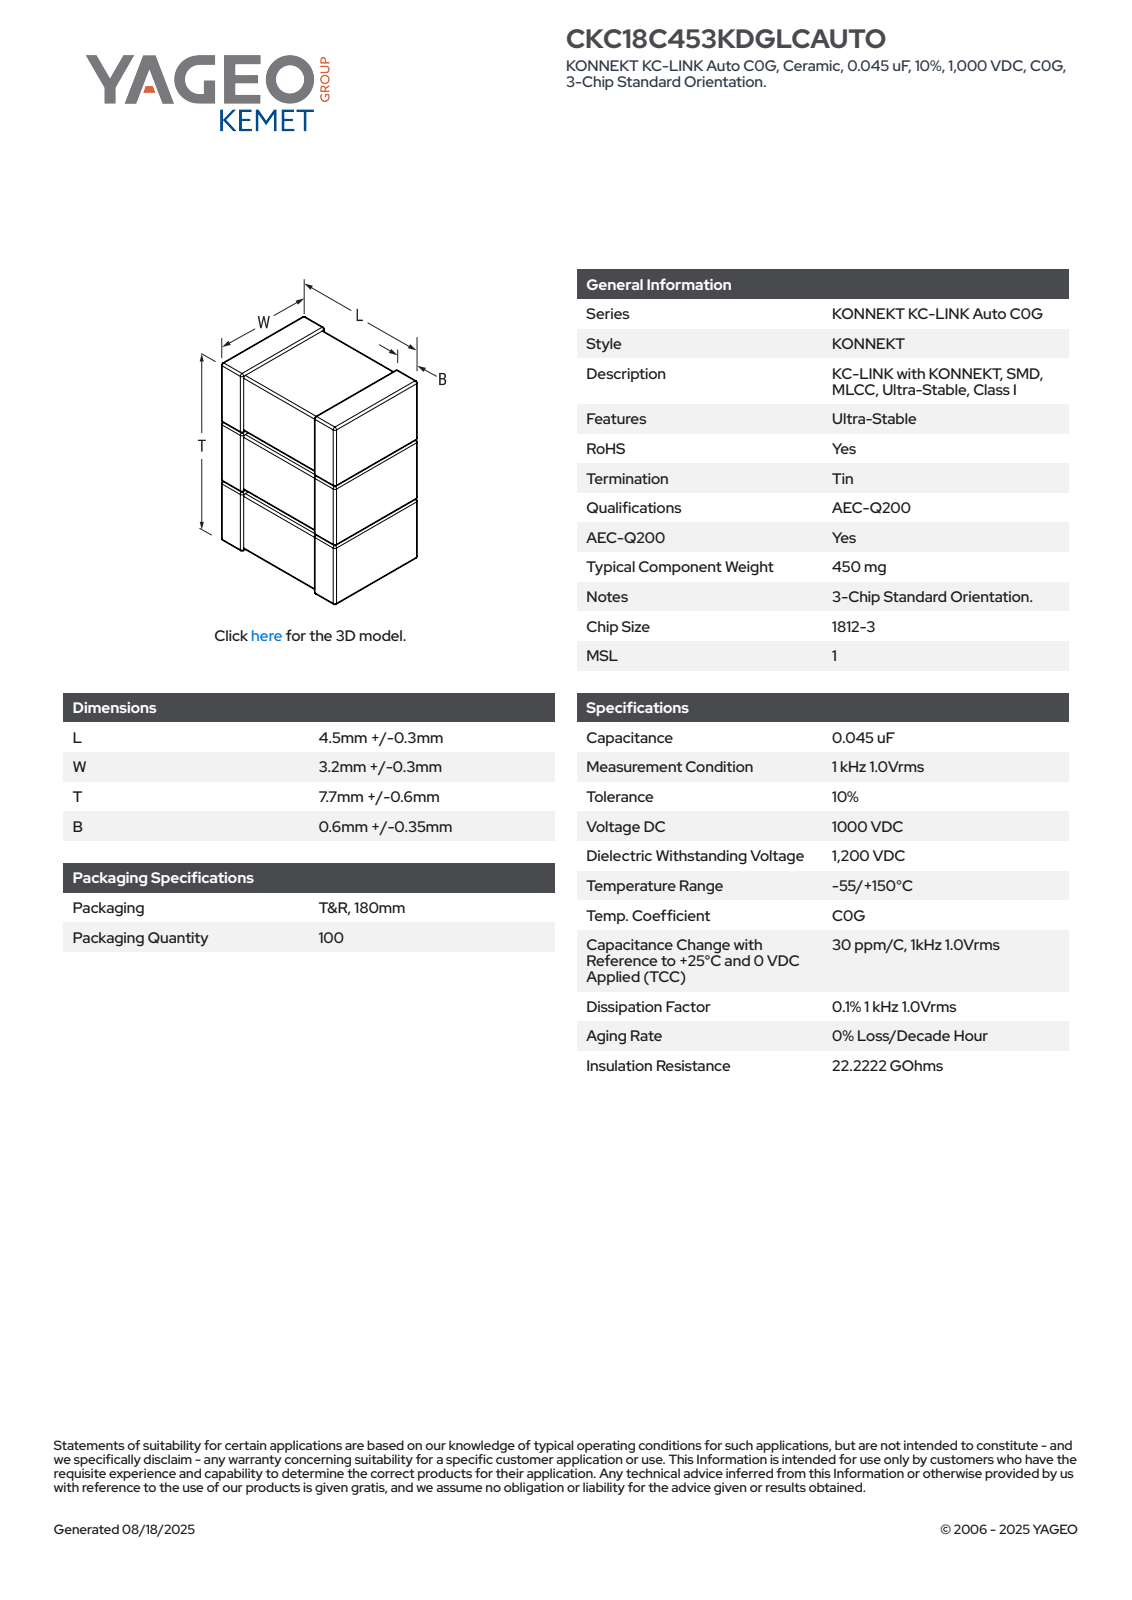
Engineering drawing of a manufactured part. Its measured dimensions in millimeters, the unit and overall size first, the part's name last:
Units: millimetres
Overall size (bounding box): 8.3 × 4.8 × 3.5
Main face-to-face distances: 2.7, 5.46, 2.77, 5.53, 2.76, 4.8, 3.43, 3.36, 5.39, 2.69
Volume: 132 mm³ · Surface area: 234 mm²
Bodies: 6 solids, 243 faces (99 planar, 96 cylindrical, 48 other)
Part name (STEP PRODUCT): CCSS_K3T_1812-3_L4.8W3.5B0.95T8.3
STEP written by: SolidWorks 2021 (AUTOMOTIVE_DESIGN)
